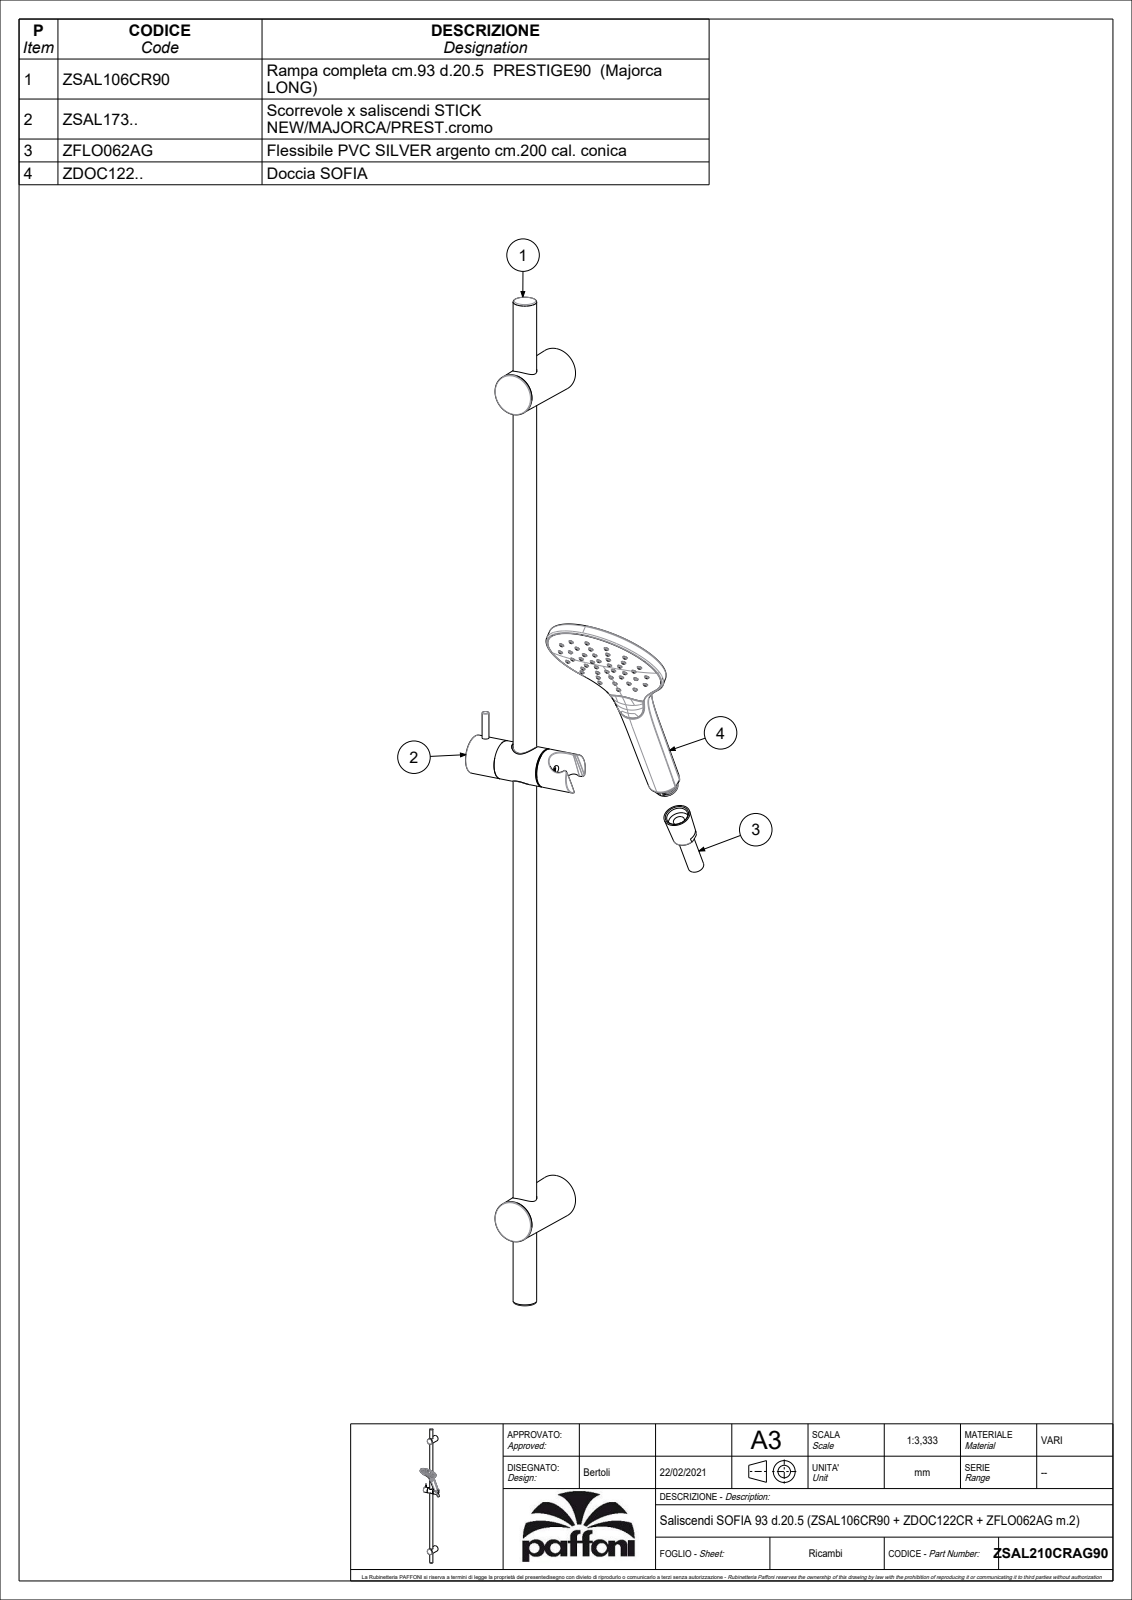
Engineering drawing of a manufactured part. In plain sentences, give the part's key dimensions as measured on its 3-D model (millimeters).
The part is named "4071643CRL_A; 4071643CRL_B; 4071643CRL_C; 4071643CRL_D (+8 more)". Its 3-D file was written by "CREO PARAMETRIC BY PTC INC, 2020044 (CONFIG_CONTROL_DESIGN)". It is 35 solids with 3913 faces: 1049 planar, 832 cylindrical and 2032 other. Overall it measures 934 by 210.2 by 147.06 millimeters. Its volume is 197 041 cubic millimeters and its surface area 326 875 square millimeters. Round holes: 5 of diameter 4, 4 of diameter 6, 3 of diameter 3, 2 of diameter 5.4, 2 of diameter 10, 2 of diameter 11, 2 of diameter 11.2, 2 of diameter 21, 2 of diameter 22.5, 2 of diameter 27, 2 of diameter 31, 1 of diameter 0.7. Round bosses or shafts: 5 of diameter 7, 3 of diameter 31.2, 3 of diameter 12, 2 of diameter 36.5, 2 of diameter 35, 2 of diameter 25, 2 of diameter 22.4, 2 of diameter 20.5. Partial cylindrical surfaces (rounded edges, fillets, slot ends): 48 of radius 0.2, 46 of radius 0.5, 27 of radius 0.3, 23 of radius 1, 14 of radius 1.5, 12 of radius 19, 10 of radius 0.6, 8 of radius 18.5. The main face-to-face distances are 1.1, 495.11, 496.21, 494.01, 74, 2.5, 2, 3, 1.5, 41.2. The hole center spacings are 36, 15.92, 20.31, 24.87, 37.41, 38.65, 44.92, 48.
